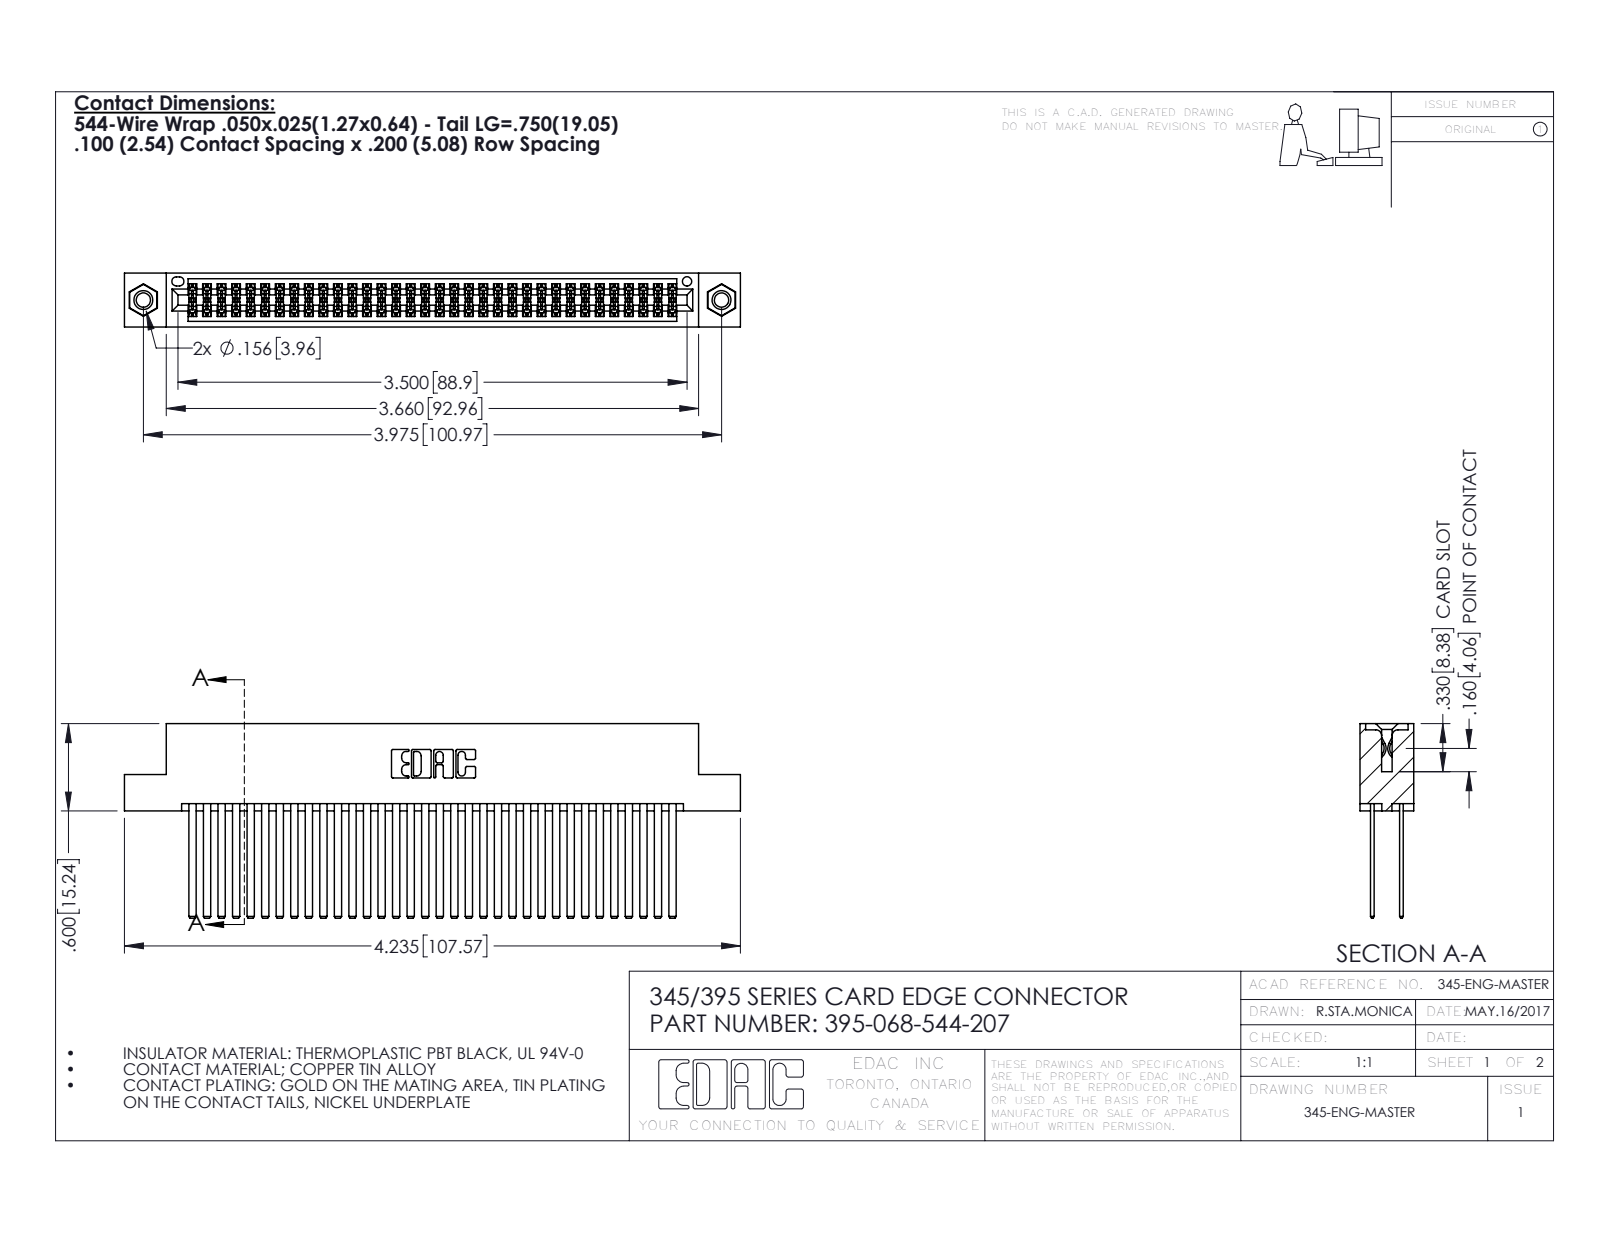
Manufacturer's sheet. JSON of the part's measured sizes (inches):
{"part_name": "345-250-001_345-250-005-103; 345 Part_Flush Mounting Lugs - 0.156 Dia-TI; 395-068-544-207; 345-292-001_345-293-144", "step_written_by": "SolidWorks 2016 (CONFIG_CONTROL_DESIGN)", "units": "inches", "bodies": {"solids": 71, "faces": 3178, "planar": 2084, "cylindrical": 1078, "other": 16}, "overall_size": [4.235, 1.337, 0.37], "volume_in3": 0.69, "surface_area_in2": 30.06, "round_holes": [[0.098, 2], [0.125, 2], [0.156, 2], [0.064, 1]], "round_bosses_or_shafts": [[0.155, 2]], "partial_cylinders_radius": [[0.006, 102], [0.01, 22], [0.007, 6], [0.031, 6], [0.026, 3], [0.014, 2], [0.019, 2], [0.022, 2]], "face_to_face_distances": [0.2, 0.025, 0.072, 0.098, 0.272, 0.298, 0.225, 0.175, 0.37, 0.05], "hole_center_spacings": [0.27, 3.74, 3.975]}
